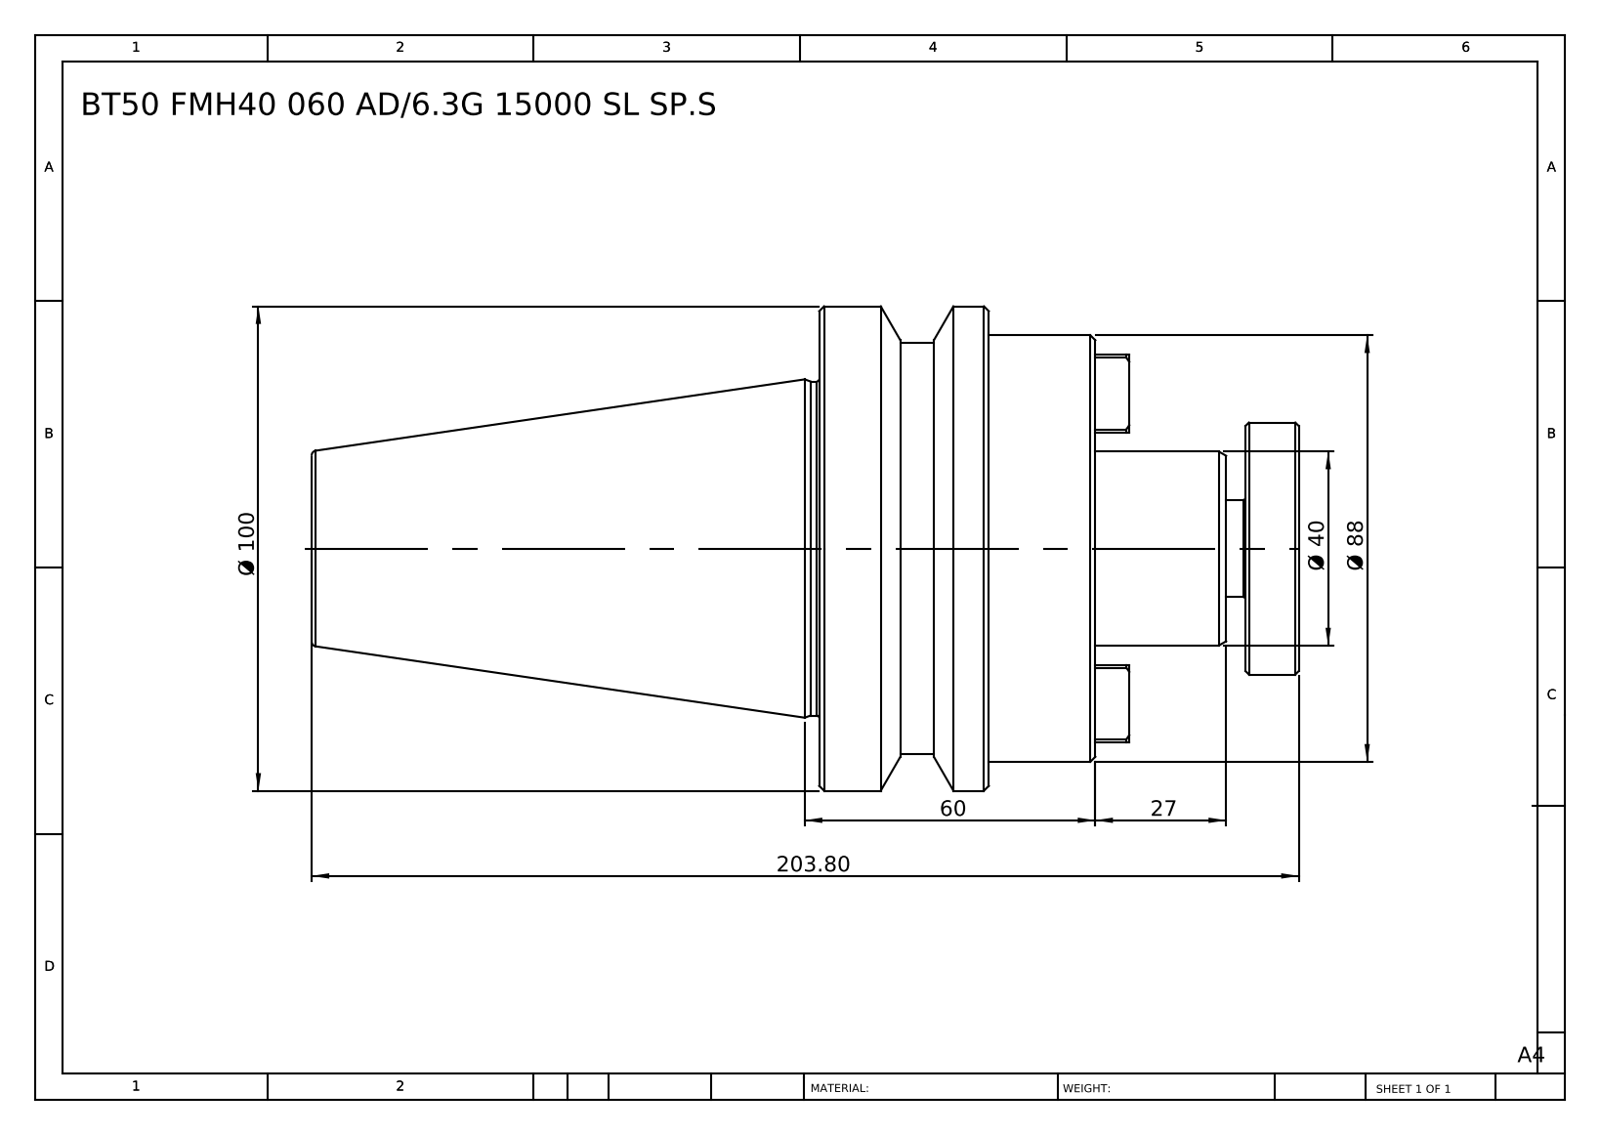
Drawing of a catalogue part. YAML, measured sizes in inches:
part_name: "BT50 FMH40 060 AD-6.3G 15000 SL SP.S"
step_written_by: "SolidWorks 2014 (CONFIG_CONTROL_DESIGN)"
units: inches
bodies: {solids: 1, faces: 77, planar: 35, cylindrical: 16, other: 26}
overall_size: [8.024, 3.937, 3.937]
volume: 43.07
surface_area: 92.98
round_bosses_or_shafts:
  - {diameter: 3.937, count: 1}
  - {diameter: 3.465, count: 1}
  - {diameter: 3.346, count: 1}
  - {diameter: 2.717, count: 1}
  - {diameter: 2.047, count: 1}
  - {diameter: 1.575, count: 1}
  - {diameter: 0.787, count: 1}
face_to_face_distances: [2.244, 2.52, 1.654, 3.898, 1.378, 0.433, 1.22, 3.465, 2.087, 0.866]
